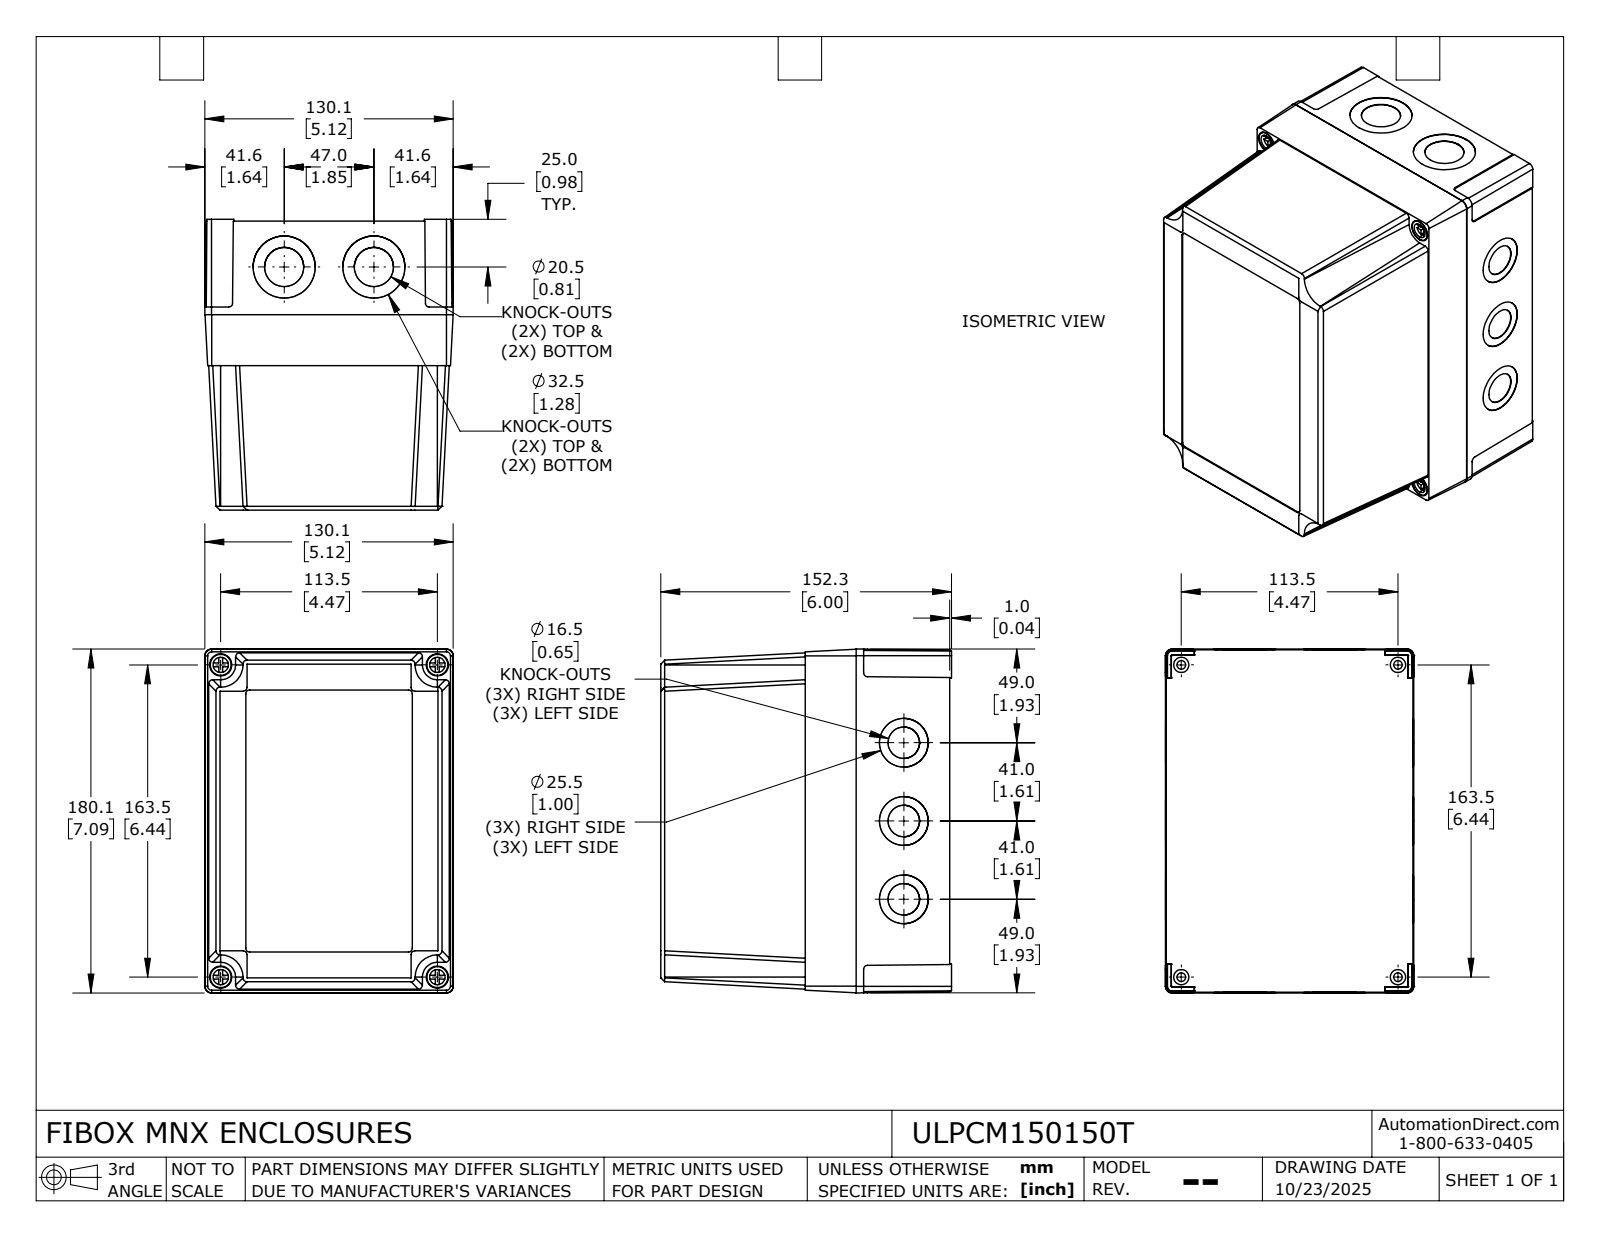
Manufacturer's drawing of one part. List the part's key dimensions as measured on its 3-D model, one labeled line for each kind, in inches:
Part name (STEP PRODUCT): ULPCM150150T_Default
STEP written by: SolidWorks 2024 (CONFIG_CONTROL_DESIGN)
Units: inches
Bodies: 6 solids, 585 faces (339 planar, 200 cylindrical, 46 other)
Overall size (bounding box): 7.091 × 5.996 × 5.122
Volume: 24.6 in³ · Surface area: 426.5 in²
Round holes (diameter × count): ⌀0.126 ×8, ⌀0.157 ×8, ⌀0.65 ×6, ⌀1.004 ×6, ⌀0.177 ×4, ⌀0.315 ×4, ⌀0.457 ×4, ⌀0.807 ×4, ⌀1.28 ×4
Round bosses / shafts (diameter × count): ⌀0.315 ×8, ⌀0.098 ×8, ⌀0.433 ×4, ⌀0.283 ×4
Partial cylindrical surfaces — rounded edges, fillets, slot ends (radius × count): R0.079 ×8, R0.083 ×8, R0.056 ×6, R0.021 ×4, R0.197 ×4, R0.023 ×2
Main face-to-face distances: 0.079, 0.118, 5.839, 0.165, 5.72, 0.098, 5.937, 5.819, 0.101, 0.022
Hole centre spacings: 1.333, 1.614, 1.939, 1.969, 2.281, 3.252, 3.276, 4.054
